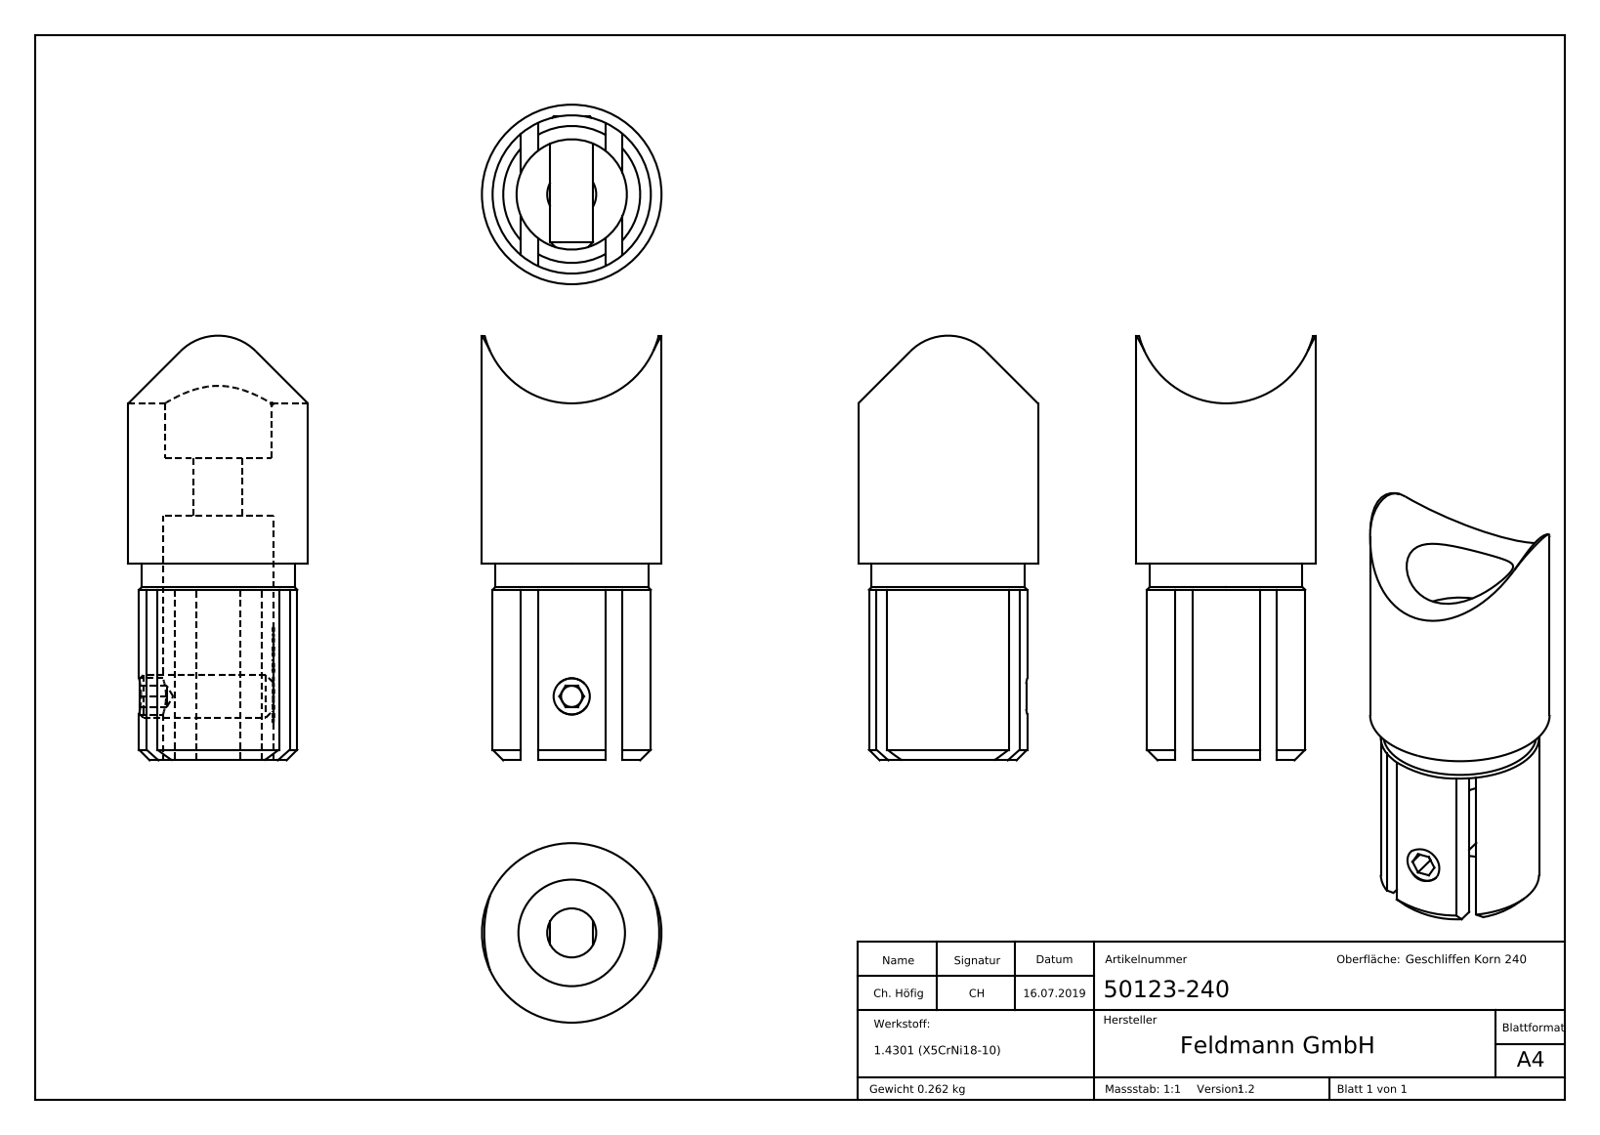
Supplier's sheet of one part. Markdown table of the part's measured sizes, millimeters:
| quantity | value |
| --- | --- |
| part name | 50123-240; 5012X-240 Teil1_50123-240 Teil1; DIN913_DIN 913 M8x25 |
| STEP written by | SolidWorks 2015 (CONFIG_CONTROL_DESIGN) |
| units | millimeters |
| bodies | 2 solids, 302 faces (131 planar, 58 cylindrical, 113 other) |
| overall size | 79.71 × 33.7 × 33.7 |
| volume | 33 150 mm³ |
| surface area | 14 305 mm² |
| round holes (diameter × count) | 6.8 × 1, 9.2 × 1, 20 × 1, 20.7 × 1 |
| round bosses / shafts (diameter × count) | 33.7 × 1, 29.7 × 1, 28.7 × 1, 8 × 1 |
| partial cylindrical surfaces (radius × count) | 10 × 1, 10.45 × 1, 16.85 × 1 |
| main face-to-face distances | 3.2, 15.8, 19, 12.6, 10.7, 9, 19.7, 37, 46, 56.7 |
